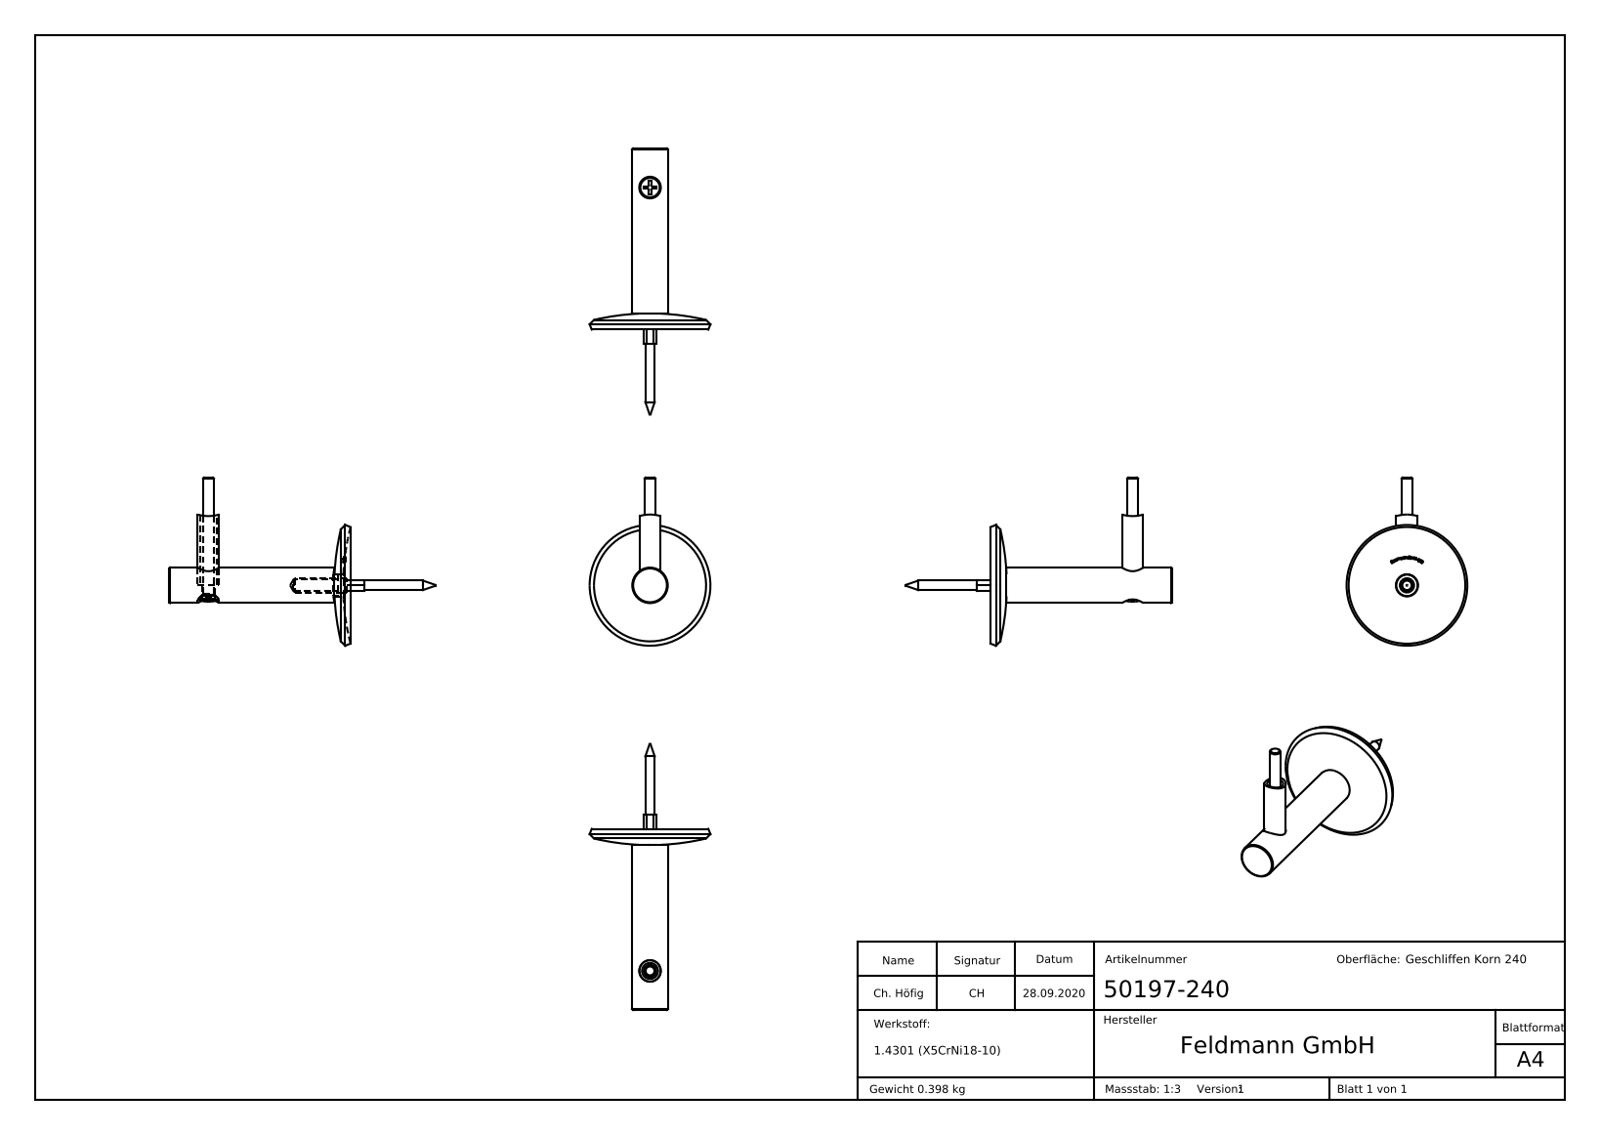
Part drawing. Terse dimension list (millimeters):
name: 50197-240 Teil3; 50197-240 Teil1; 5834X-240-XX Konfig_58341-240-80; 50197-240 (+7 more)
written by: SolidWorks 2018 (CONFIG_CONTROL_DESIGN)
unit: mm
bodies: 5 solids, 565 faces (266 planar, 32 cylindrical, 267 other)
size: 149.76 × 96.7 × 68
volume: 50 330 mm³; area: 21 443 mm²
holes: 1× ⌀6.8, 1× ⌀7, 1× ⌀9, 1× ⌀12.1, 1× ⌀12.2, 1× ⌀12.5
bosses: 2× ⌀12, 1× ⌀20, 1× ⌀10.91, 1× ⌀8, 1× ⌀6, 1× ⌀5.3
rounds: 4× R1, 1× R21.2
face distances: 6, 95, 3, 25.24, 69.76, 1.15, 63.7, 60.7, 57.7, 4.76
